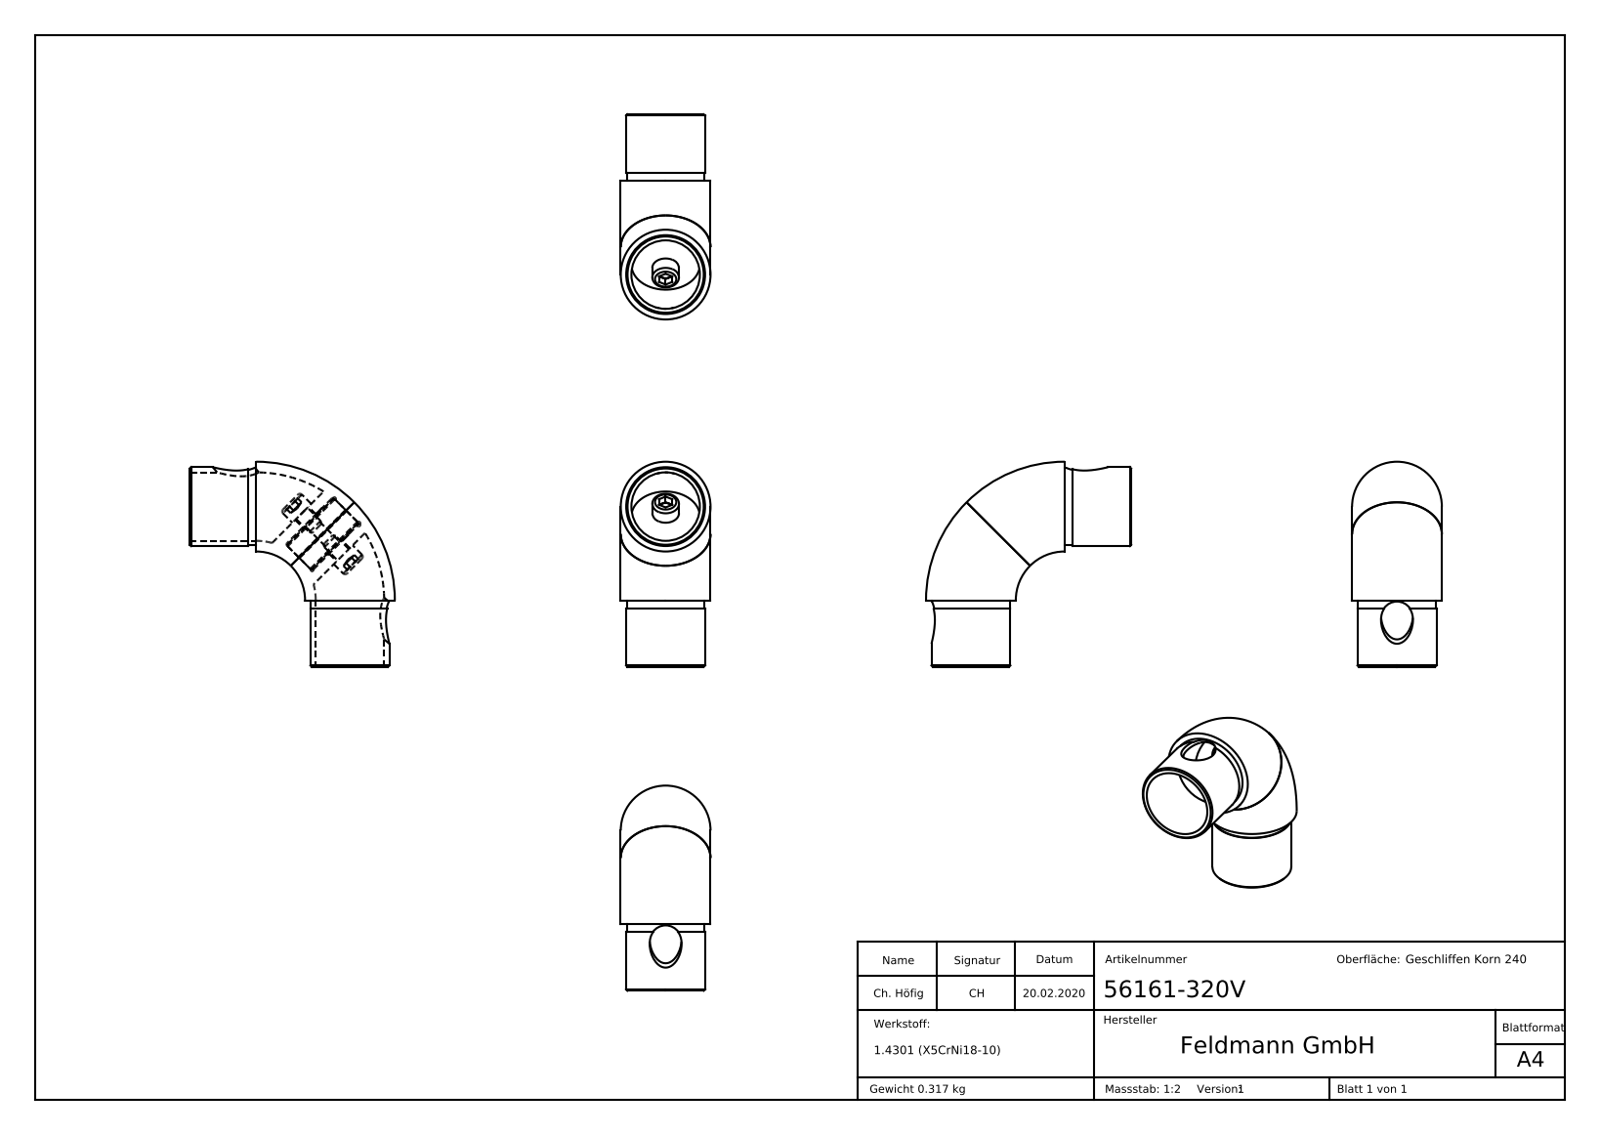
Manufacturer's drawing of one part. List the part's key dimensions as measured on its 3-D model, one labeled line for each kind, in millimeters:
Part name (STEP PRODUCT): DIN 912 Konfig; 5616X-320V Teil2_56161-320V Teil2; 56161-320V; 5616X-320V Teil2 (+3 more)
STEP written by: SolidWorks 2015 (CONFIG_CONTROL_DESIGN)
Units: millimetres
Bodies: 5 solids, 532 faces (288 planar, 18 cylindrical, 226 other)
Overall size (bounding box): 13955.19 × 12419.37 × 10009.53
Volume: 40 150 mm³ · Surface area: 24 636 mm²
Round holes (diameter × count): ⌀7 ×2, ⌀12 ×2, ⌀25 ×2, ⌀25.7 ×2, ⌀5 ×1
Round bosses / shafts (diameter × count): ⌀29.6 ×2, ⌀29.2 ×2, ⌀10 ×2, ⌀6 ×2
Main face-to-face distances: 11, 4, 4.5, 17.5, 6.5, 7, 18, 0.5, 13.5, 22
